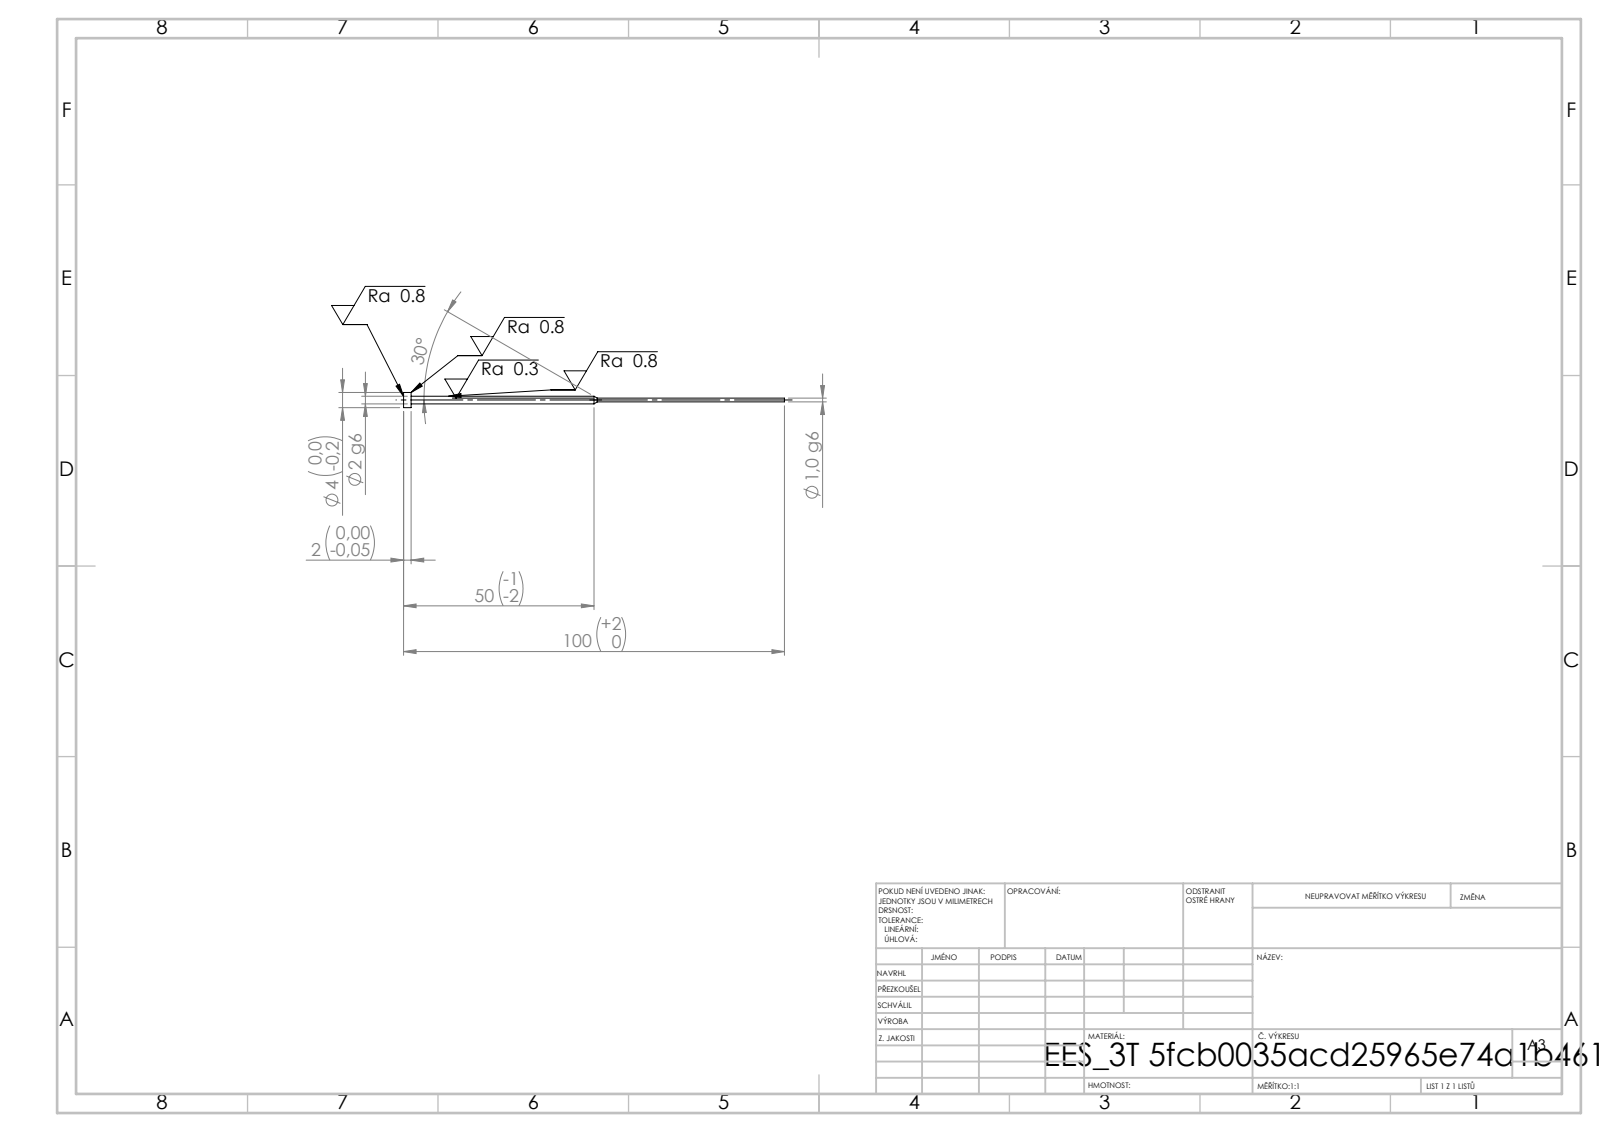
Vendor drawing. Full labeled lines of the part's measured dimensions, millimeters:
STEP written by: SolidWorks 2019 (CONFIG_CONTROL_DESIGN)
Units: millimetres
Bodies: 1 solid, 11 faces (3 planar, 6 cylindrical, 2 other)
Overall size (bounding box): 100 × 4 × 4
Volume: 216 mm³ · Surface area: 509 mm²
Round bosses / shafts (diameter × count): ⌀4 ×1, ⌀2 ×1, ⌀1 ×1
Main face-to-face distances: 2, 98, 100
